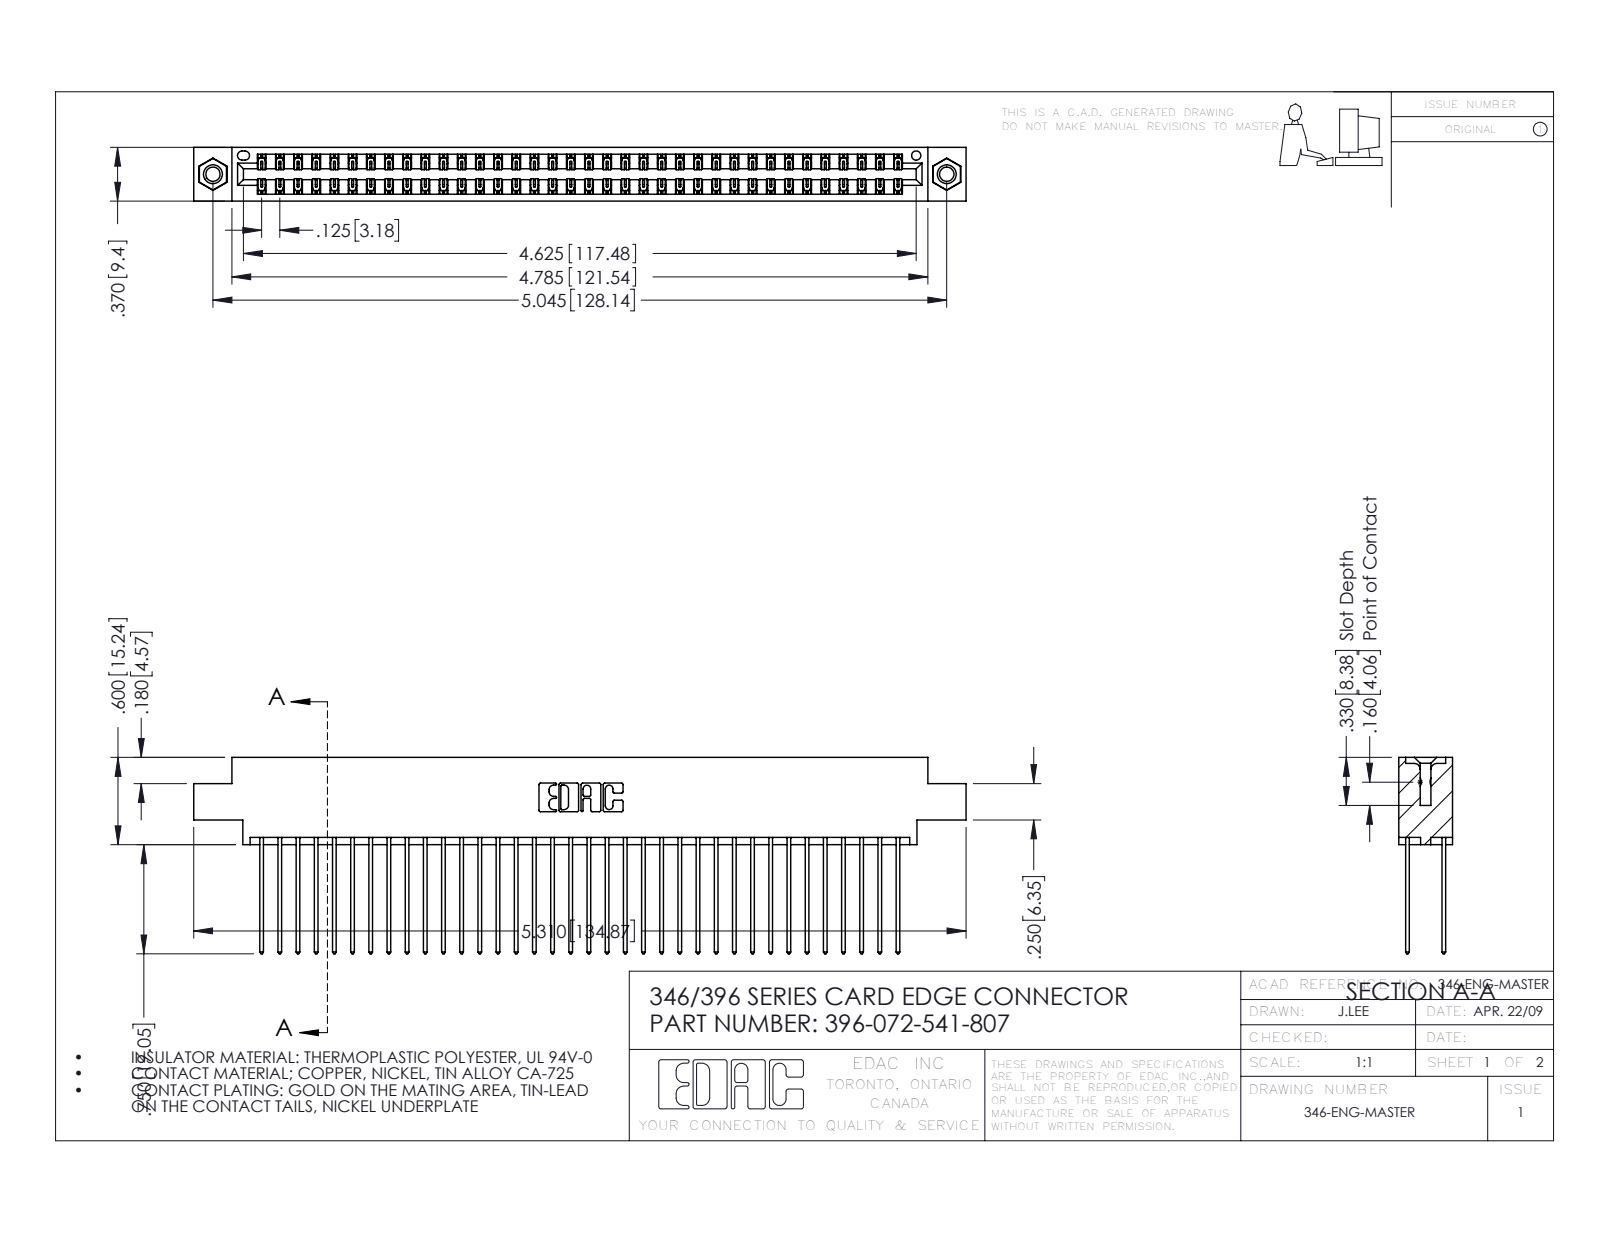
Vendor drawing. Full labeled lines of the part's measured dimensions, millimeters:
Part name (STEP PRODUCT): 346 Part_0.170 Offset - 0.156 Dia-TI; 345-250-001_345-250-005-103; 345-292-001_345-293-141; 396-072-541-807
STEP written by: SolidWorks 2016 (CONFIG_CONTROL_DESIGN)
Units: millimetres
Bodies: 75 solids, 3930 faces (2632 planar, 1282 cylindrical, 16 other)
Overall size (bounding box): 134.9 × 34.3 × 9.4
Volume: 13 400 mm³ · Surface area: 20 450 mm²
Round holes (diameter × count): ⌀2.5 ×2, ⌀3.2 ×2, ⌀4 ×2, ⌀1.6 ×1
Round bosses / shafts (diameter × count): ⌀3.9 ×2
Partial cylindrical surfaces — rounded edges, fillets, slot ends (radius × count): R0.2 ×108, R0.3 ×72, R0.3 ×22, R0.2 ×6, R0.8 ×6, R0.7 ×3, R0.4 ×2, R0.6 ×2
Main face-to-face distances: 1.2, 8.2, 6.4, 1.8, 7.6, 0.6, 9.4, 7, 5.6, 5.7
Hole centre spacings: 6.2, 122.8, 128.1
